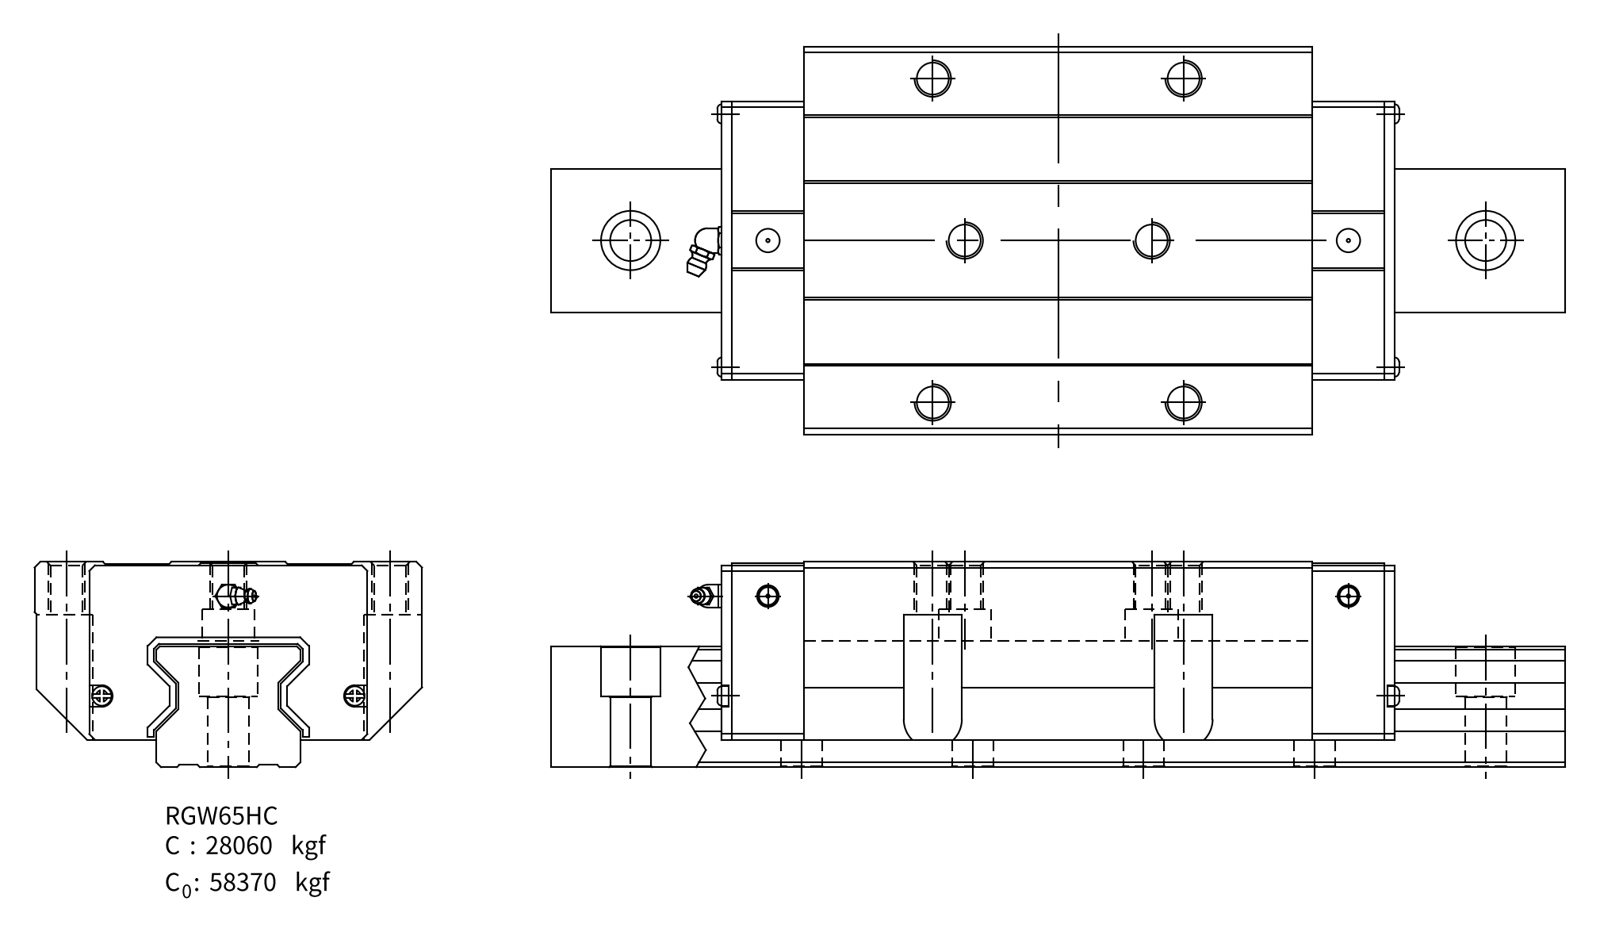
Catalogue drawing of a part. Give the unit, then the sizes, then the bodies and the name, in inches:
Units: inches
Overall size (bounding box): 14.567 × 6.693 × 3.543
Round holes (diameter × count): ⌀0.63 ×6, ⌀0.709 ×5, ⌀1.024 ×5, ⌀0.059 ×2, ⌀0.335 ×2, ⌀0.406 ×2, ⌀0.906 ×2, ⌀0.394 ×1, ⌀0.492 ×1
Partial cylindrical surfaces — rounded edges, fillets, slot ends (radius × count): R0.453 ×4, R0.039 ×2
Main face-to-face distances: 2.106, 0.039, 1.457, 2.48, 1.417, 3.504, 0.92, 3.071, 1.614, 0.374
Hole centre spacings: 2.849, 2.904, 2.953, 3.536, 3.989, 4.669, 4.701, 5.831
Volume: 225.3 in³ · Surface area: 480.8 in²
Bodies: 2 solids, 199 faces (121 planar, 68 cylindrical, 10 other)
Part name (STEP PRODUCT): RGW65HC_BLOCK_5; PRT0014; RGW65HC_ASM_5_ASM; RGW65HC_ASM
STEP written by: PRO/ENGINEER BY PARAMETRIC TECHNOLOGY CORPORATION, 2004360 (CONFIG_CONTROL_DESIGN)
